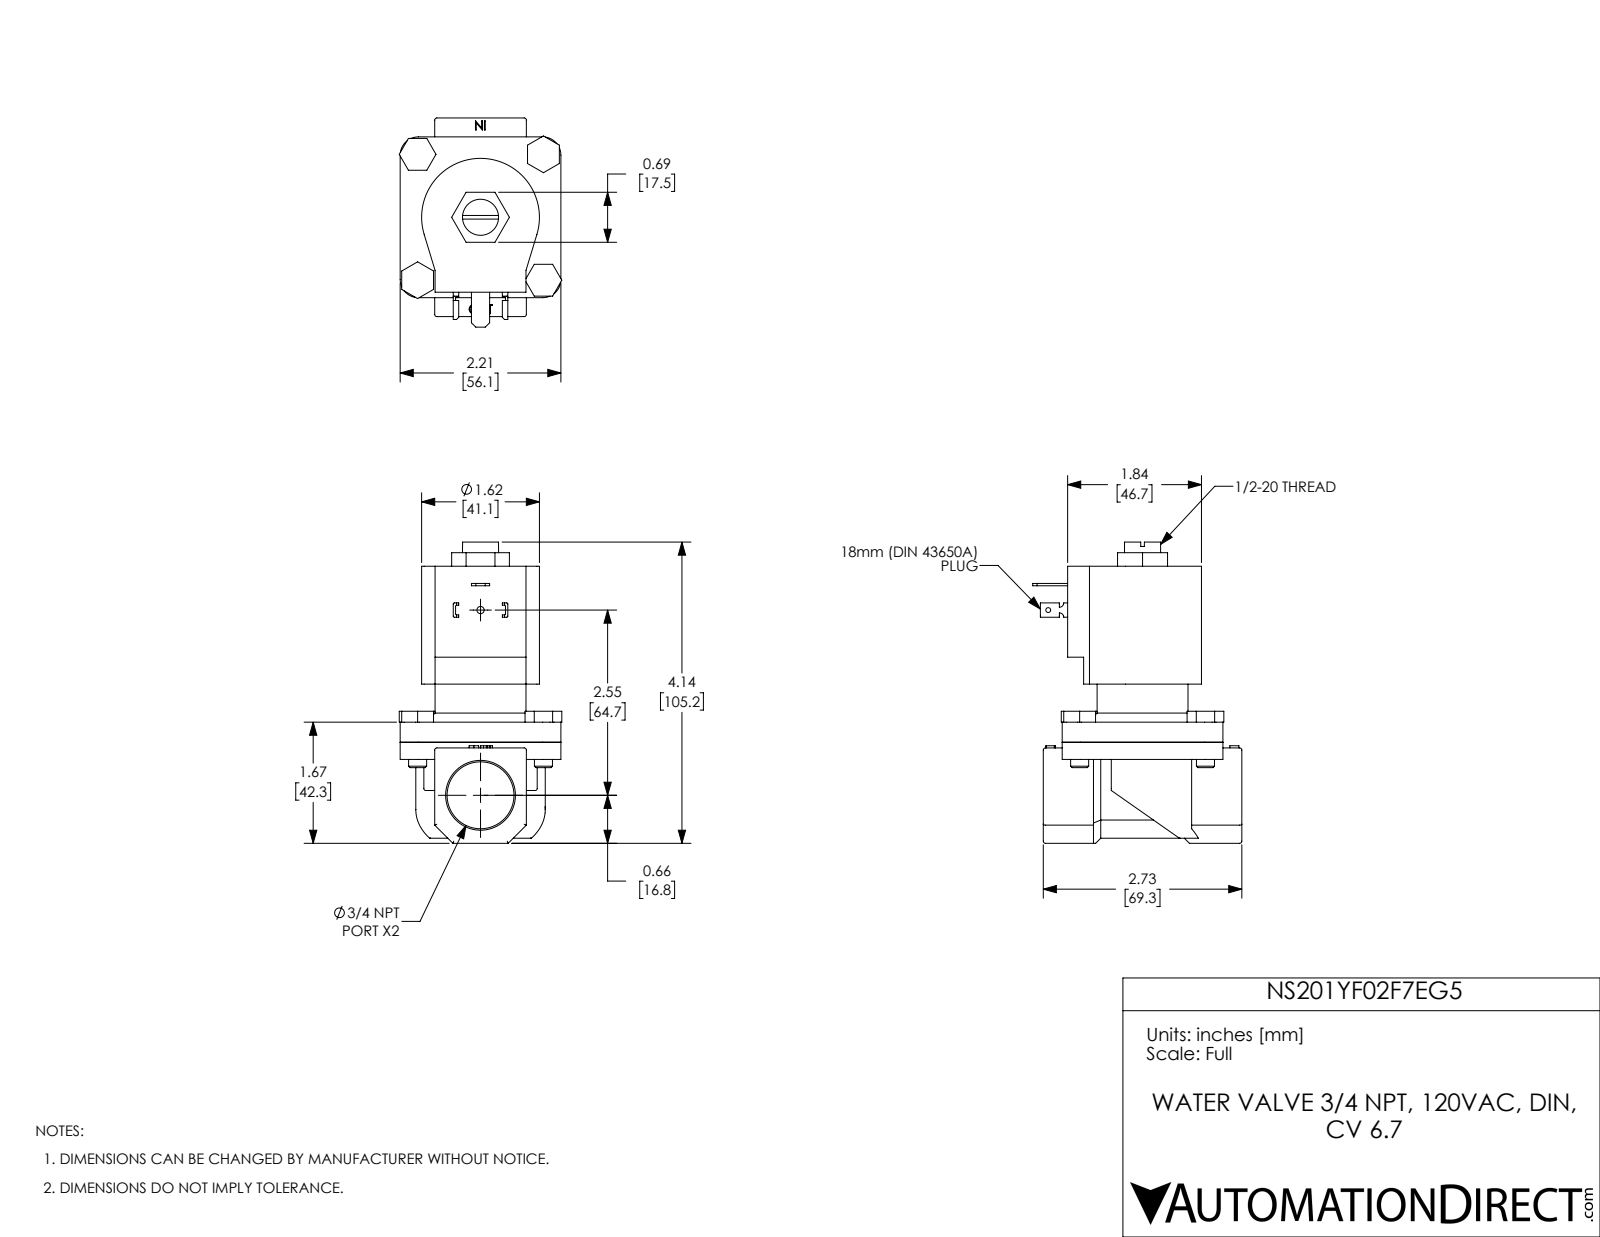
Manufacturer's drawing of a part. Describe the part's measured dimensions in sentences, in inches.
The part is named "NS201YF02F7EG5". Its 3-D file was written by "SolidWorks 2017 (AUTOMOTIVE_DESIGN)". It is 11 solids with 332 faces: 198 planar, 99 cylindrical and 35 other. Overall it measures 4.14 by 2.875 by 2.235 inches. Its volume is 10.32 cubic inches and its surface area 67.12 square inches. Round holes: 4 of diameter 0.25, 1 of diameter 0.067, 1 of diameter 0.1, 1 of diameter 0.496, 1 of diameter 0.512, 1 of diameter 0.92, 1 of diameter 1.155. Round bosses or shafts: 4 of diameter 0.248, 1 of diameter 1.25. Partial cylindrical surfaces (rounded edges, fillets, slot ends): 15 of radius 0.03, 8 of radius 0.015, 4 of radius 0.25, 2 of radius 0.06, 1 of radius 0.81, 1 of radius 0.89. The main face-to-face distances are 0.276, 2.419, 2.143, 0.475, 1.735, 2.21, 0.236, 0.512, 2.655, 0.26. The hole center spacings are 1.223, 1.73, 2.446, 2.546.
